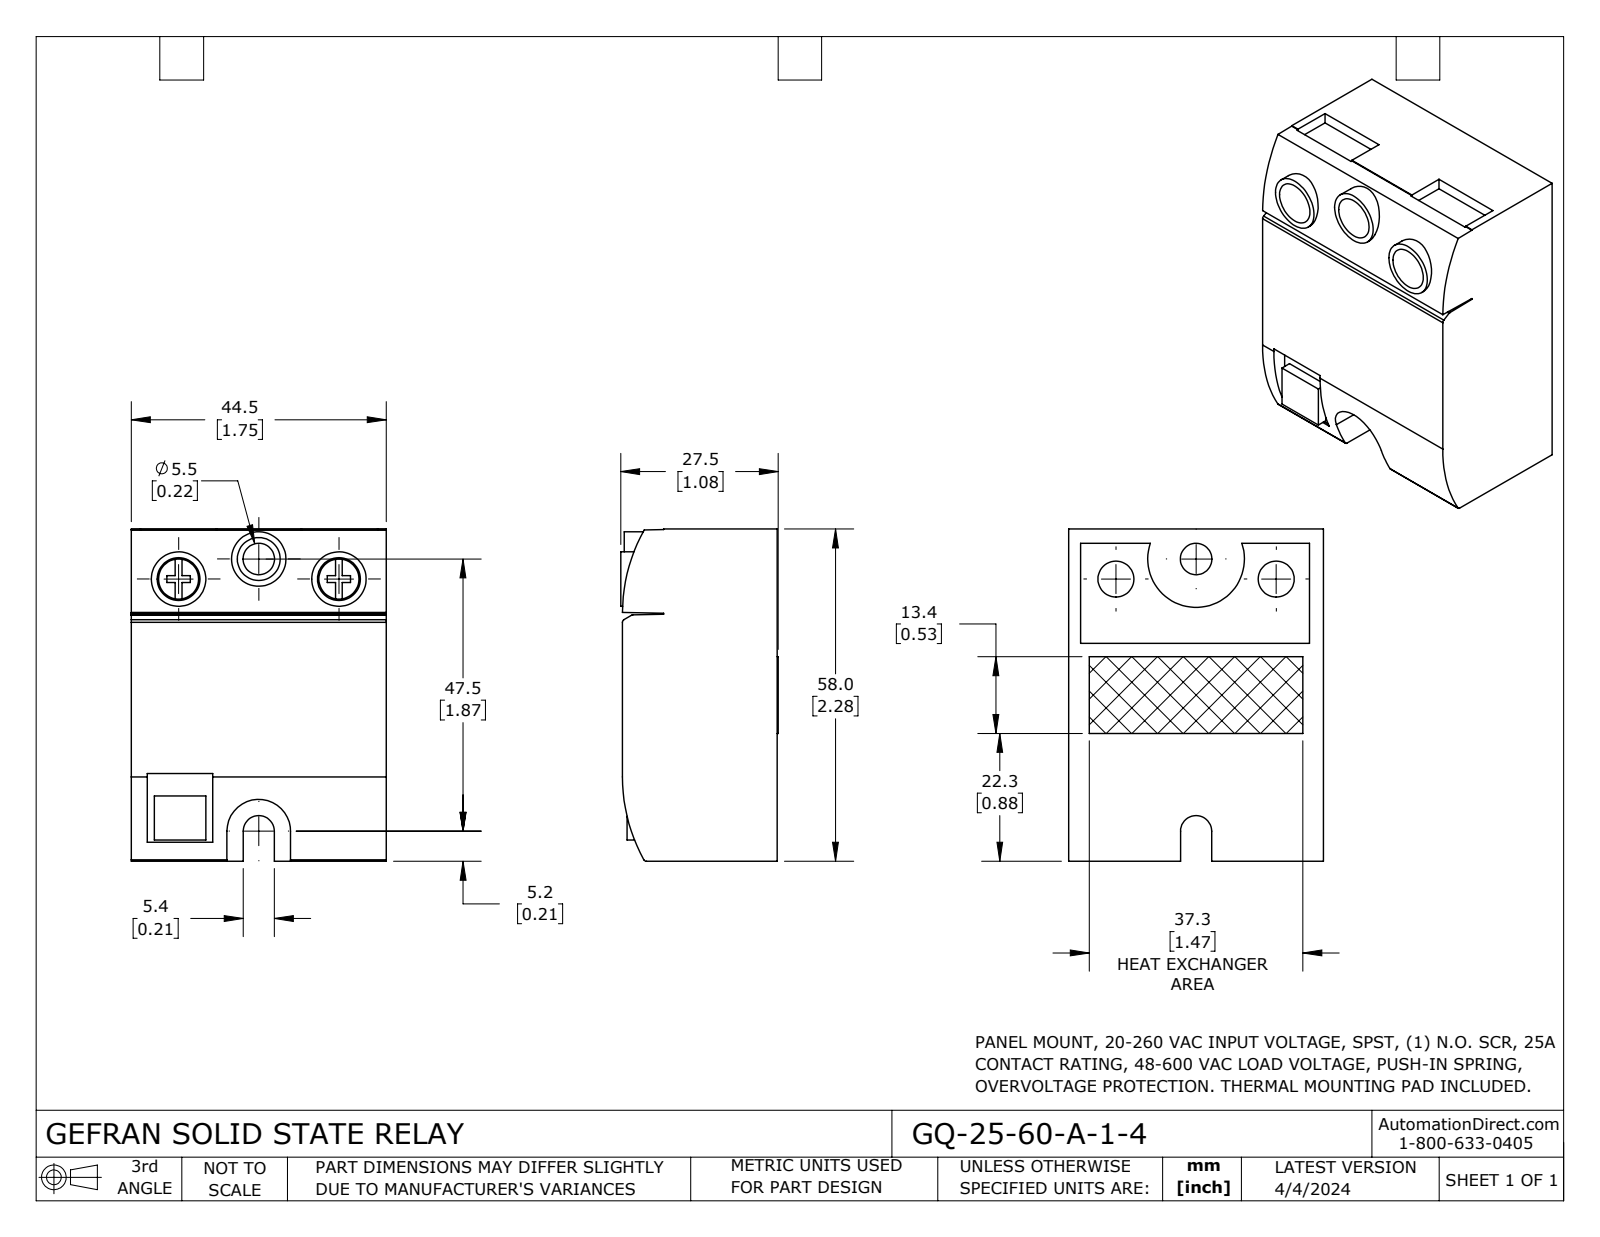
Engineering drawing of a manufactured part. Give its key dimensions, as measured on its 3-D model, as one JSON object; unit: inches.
{"part_name": "GQ-25-60-A-1-4", "step_written_by": "SolidWorks 2023 (CONFIG_CONTROL_DESIGN)", "units": "inches", "bodies": {"solids": 1, "faces": 120, "planar": 85, "cylindrical": 35, "other": 0}, "overall_size": [2.283, 1.752, 1.083], "volume_in3": 3.801, "surface_area_in2": 20.63, "round_holes": [[0.295, 3], [0.217, 1]], "round_bosses_or_shafts": [[0.374, 3], [0.276, 2], [0.247, 2]], "partial_cylinders_radius": [[0.02, 3], [1.171, 2], [0.107, 1], [0.219, 1], [0.332, 1]], "face_to_face_distances": [1.752, 1.063, 2.283, 0.11, 1.071, 0.118, 0.953, 0.657, 1.094, 2.205], "hole_center_spacings": [0.568, 1.102]}
